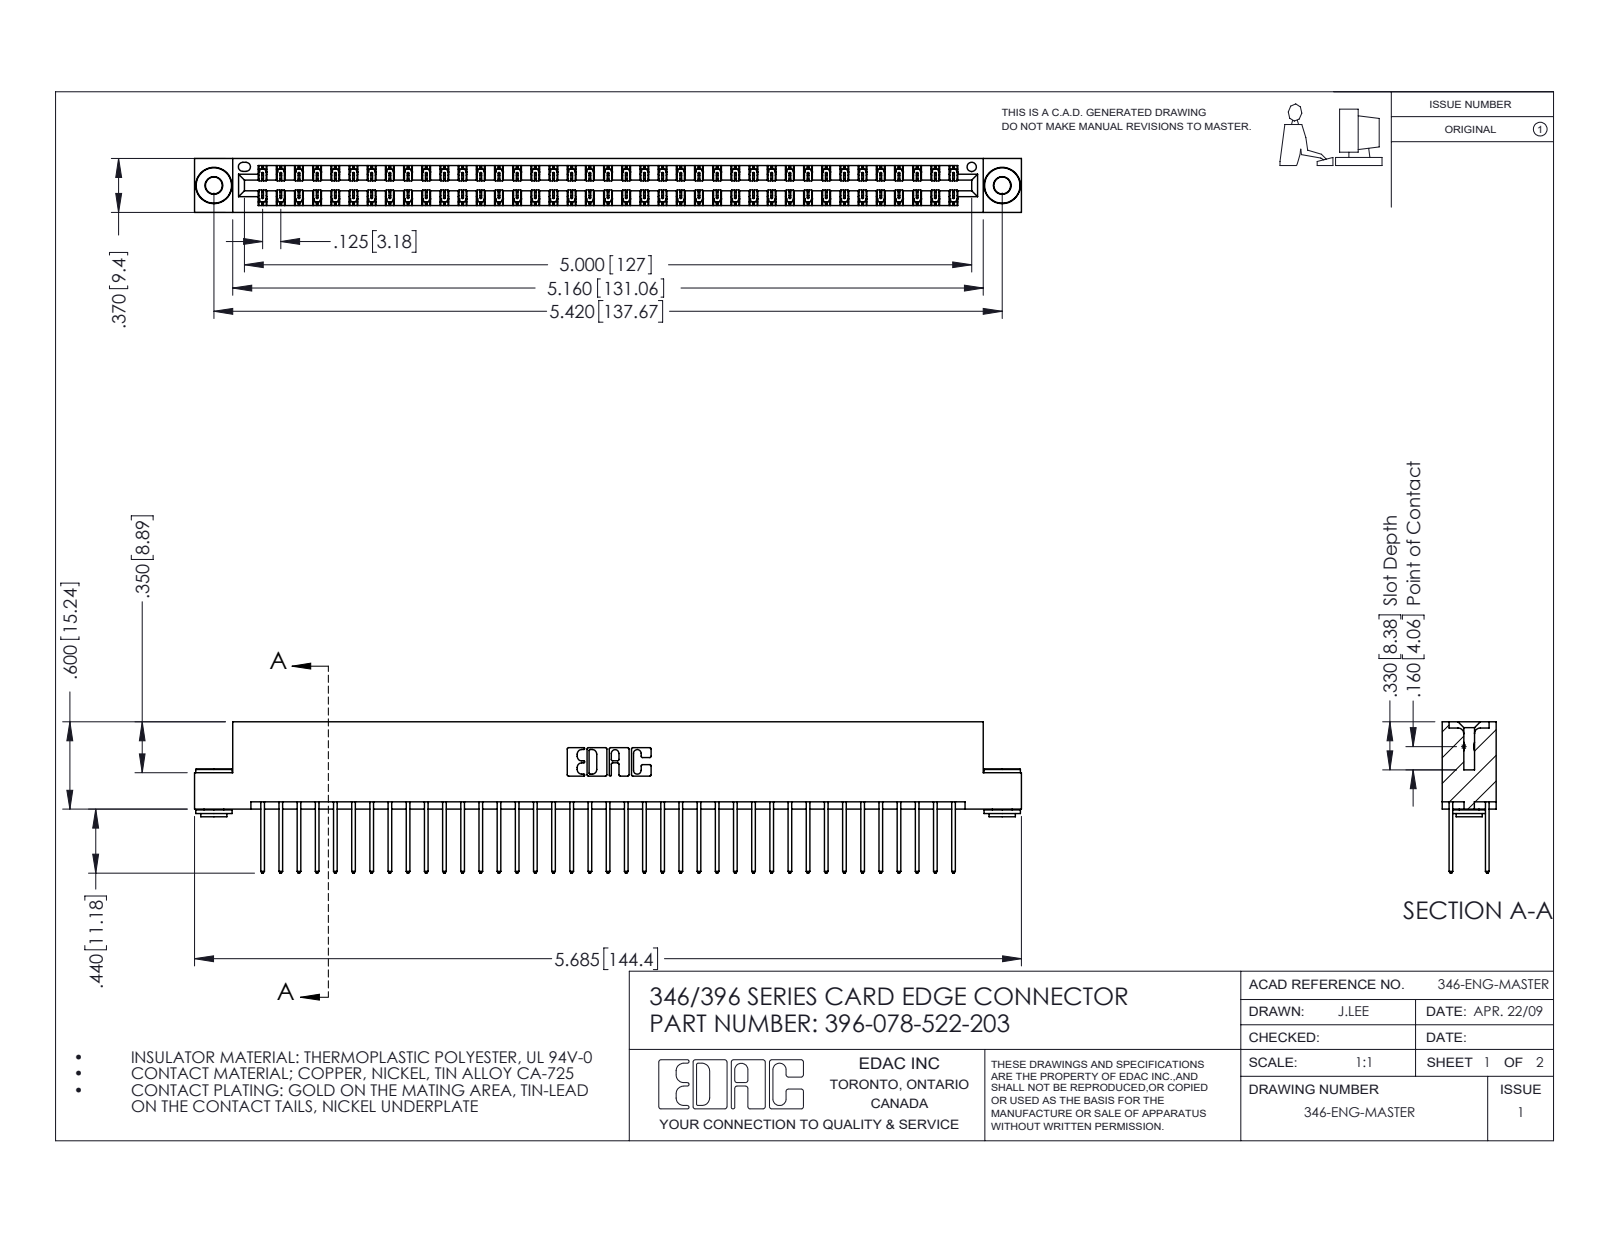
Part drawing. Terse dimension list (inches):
name: 396-078-522-203; 346 Part_Flush Mounting Lugs - 0.156 Dia-TH; 345-250-002_345-250-002-102; 345-292-001_345-293-122
written by: SolidWorks 2016 (CONFIG_CONTROL_DESIGN)
unit: in
bodies: 81 solids, 4216 faces (2816 planar, 1392 cylindrical, 8 other)
size: 5.685 × 1.04 × 0.37
volume: 0.871 in³; area: 32.11 in²
holes: 2× ⌀0.116, 2× ⌀0.156, 1× ⌀0.064
bosses: 2× ⌀0.25, 2× ⌀0.18, 2× ⌀0.136
rounds: 117× R0.006, 78× R0.01, 22× R0.01, 6× R0.007, 6× R0.031, 3× R0.026, 2× R0.014, 2× R0.022
face distances: 0.048, 0.322, 0.25, 0.025, 0.37, 0.072, 0.298, 0.275, 0.148, 0.222
hole spacings: 0.246, 5.211, 5.42
